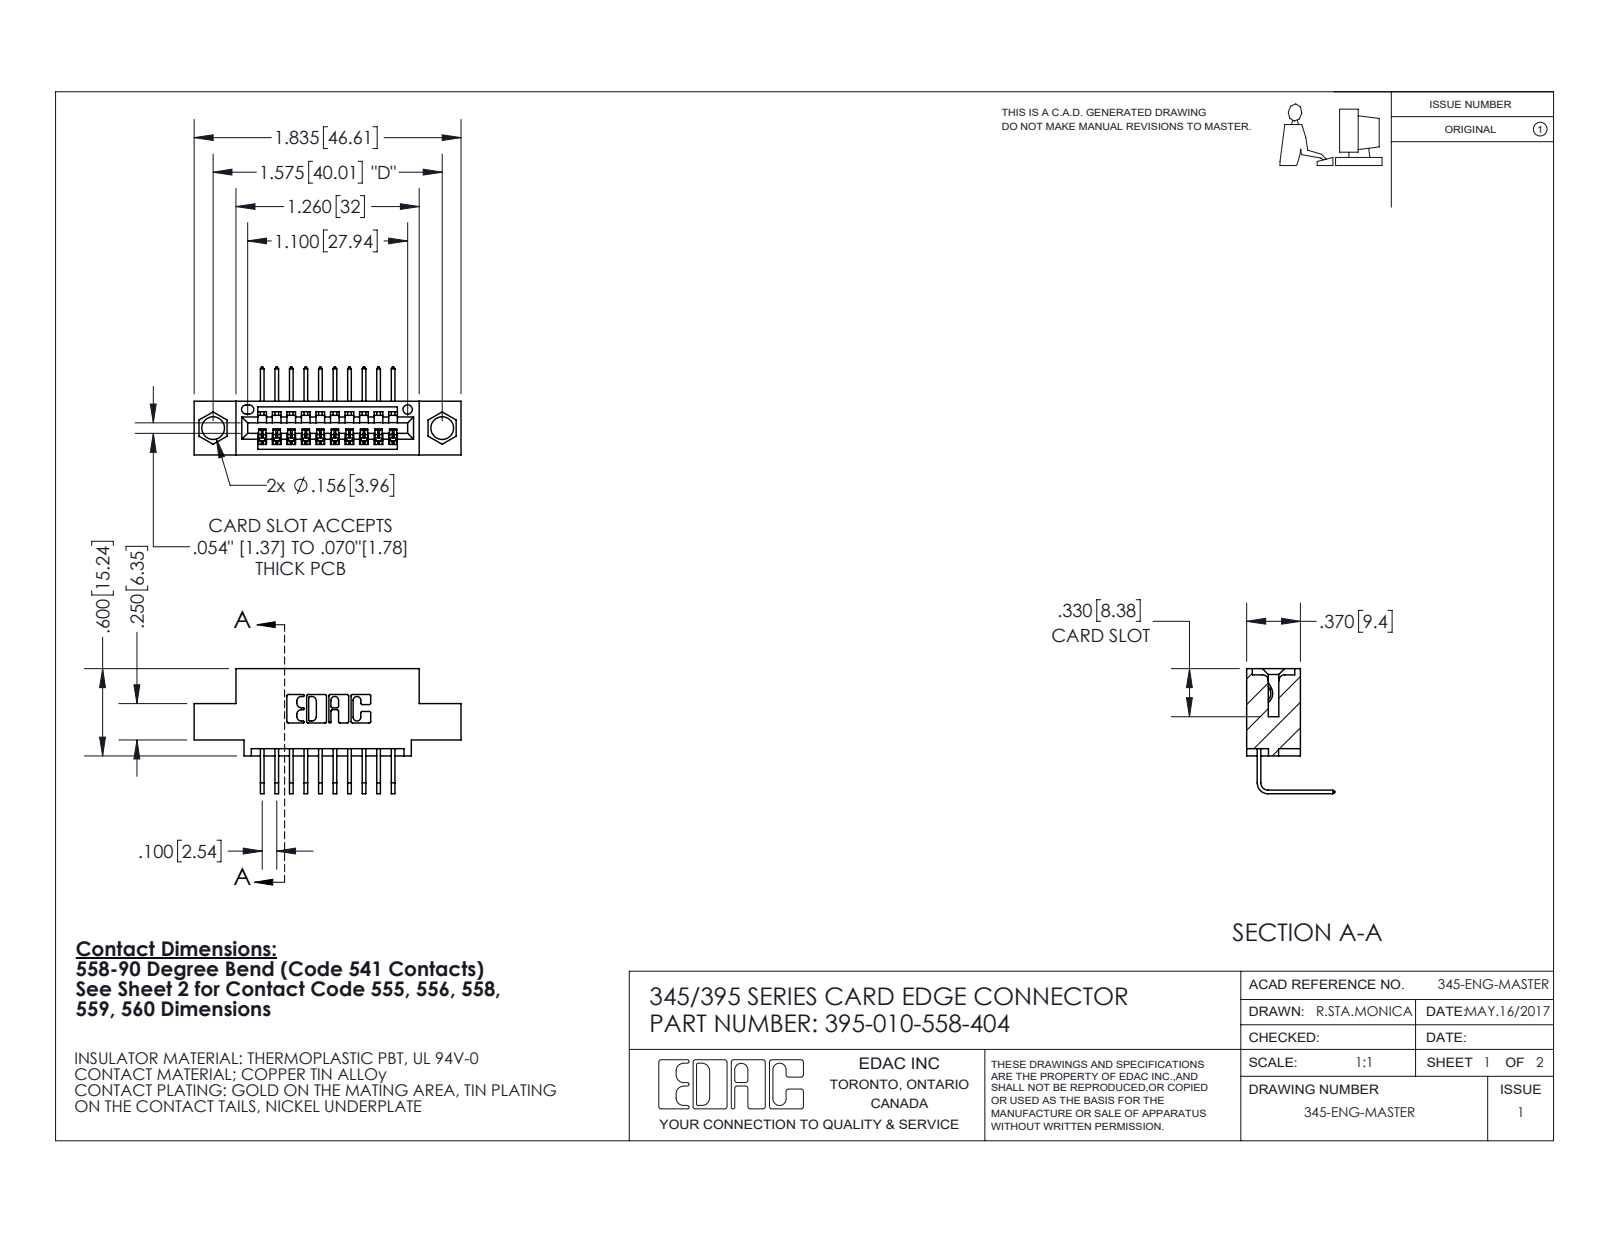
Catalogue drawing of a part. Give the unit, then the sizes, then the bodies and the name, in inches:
Units: inches
Overall size (bounding box): 1.835 × 0.859 × 0.605
Round holes (diameter × count): ⌀0.156 ×2, ⌀0.064 ×1
Partial cylindrical surfaces — rounded edges, fillets, slot ends (radius × count): R0.01 ×22, R0.006 ×20, R0.007 ×6, R0.031 ×6, R0.026 ×3, R0.031 ×2, R0.04 ×2, R0.014 ×1
Main face-to-face distances: 0.2, 0.072, 0.298, 0.37, 0.1, 0.098, 0.272, 0.025, 0.6, 0.06
Hole centre spacings: 0.27, 1.344, 1.575
Volume: 0.245 in³ · Surface area: 7.79 in²
Bodies: 11 solids, 744 faces (518 planar, 226 cylindrical, 0 other)
Part name (STEP PRODUCT): 345-292-001_558 Tail - 2; 395-010-558-404; 345 Part_0.110 Offset - 0.156 Dia-TI
STEP written by: SolidWorks 2020 (CONFIG_CONTROL_DESIGN)
